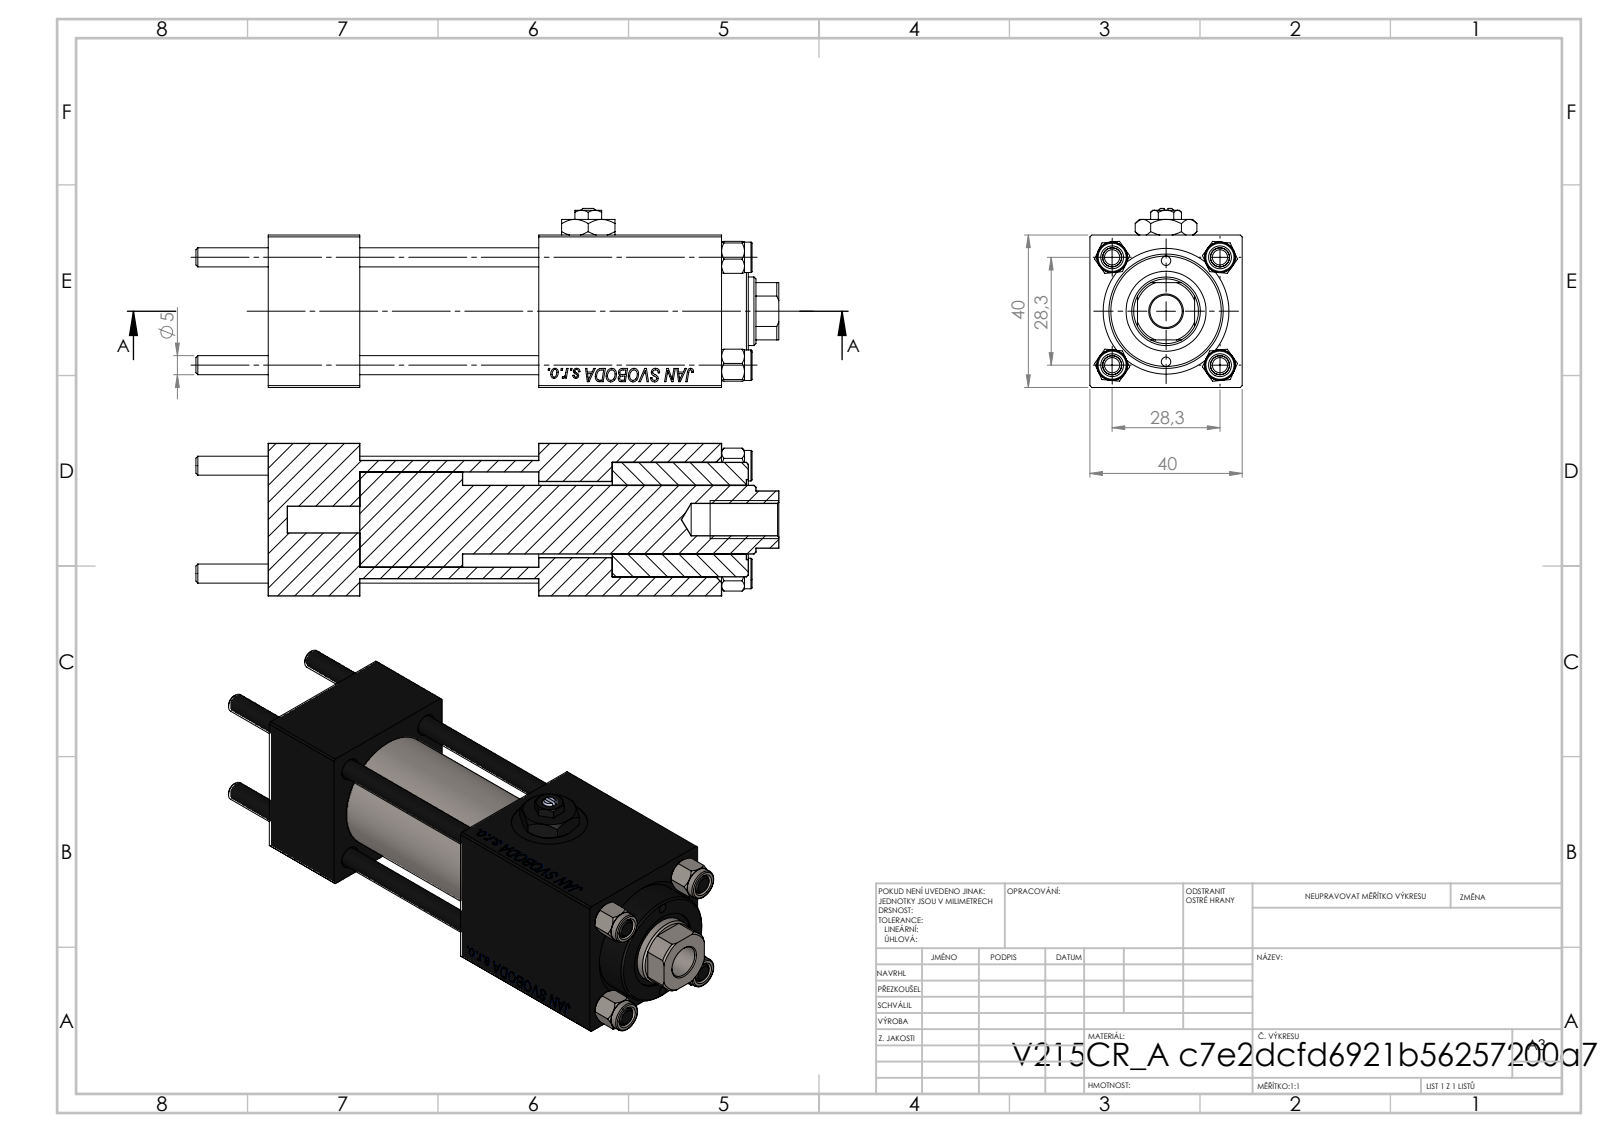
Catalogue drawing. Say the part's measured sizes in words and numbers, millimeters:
The part is named "Zatka_pro_OIL_PORT; V215CR_BODY_A; V215CR_VCP; CR025_012_A_0_G_A_G_M_020_+#_##_TYCINKA (+2 more)". Its 3-D file was written by "SolidWorks 2019 (CONFIG_CONTROL_DESIGN)". It is 12 solids with 1182 faces: 542 planar, 84 cylindrical and 556 other. Overall it measures 153 by 47 by 40 millimeters. Its volume is 151 662 cubic millimeters and its surface area 62 079 square millimeters. Round holes: 4 of diameter 5, 3 of diameter 20, 2 of diameter 2.5, 2 of diameter 7, 2 of diameter 13.16, 1 of diameter 8.5, 1 of diameter 18, 1 of diameter 21, 1 of diameter 25, 1 of diameter 30. Round bosses or shafts: 4 of diameter 8, 1 of diameter 31. Partial cylindrical surfaces (rounded edges, fillets, slot ends): 1 of radius 8.5. The main face-to-face distances are 40, 24, 47, 71, 90.3, 66.3, 19.3, 48, 119, 95. The hole center spacings are 14.18, 20.01, 28.3, 30.84, 13.25, 40.02, 26.5, 72.
